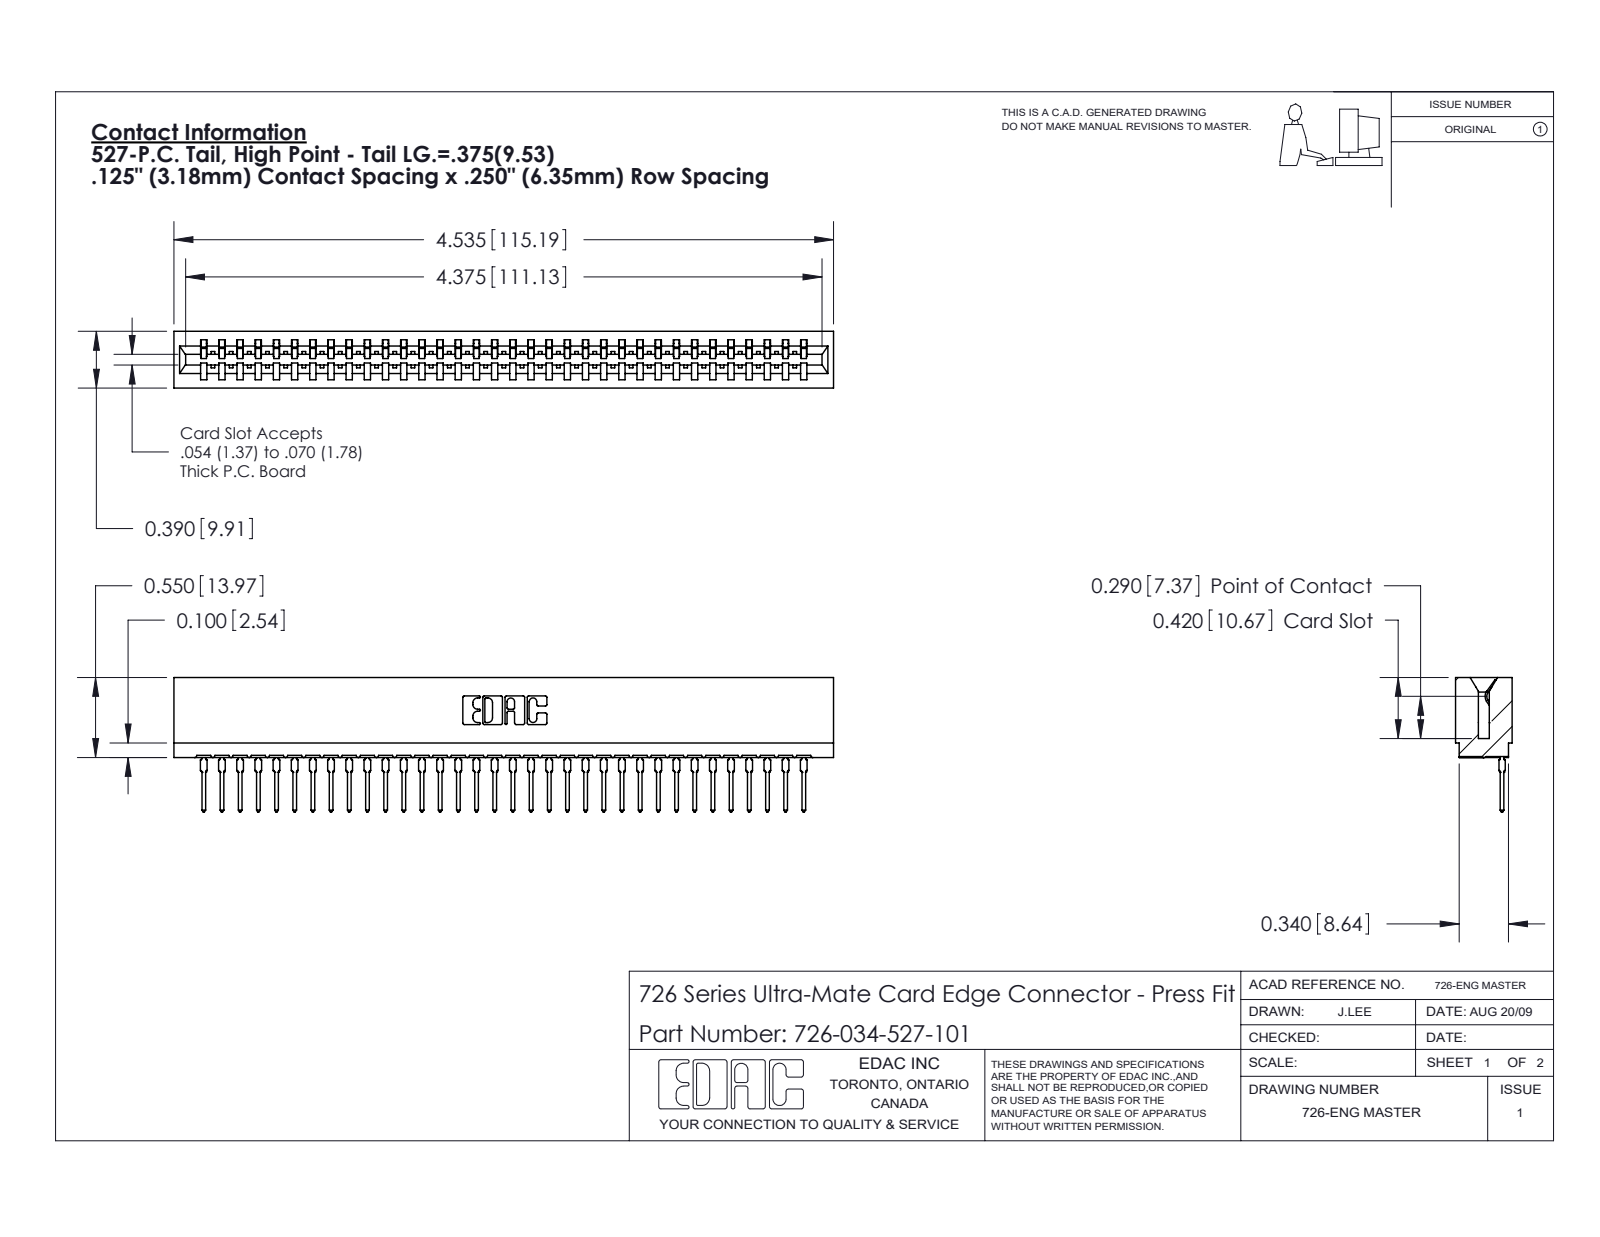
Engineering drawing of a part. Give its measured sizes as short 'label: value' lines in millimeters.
name: 726 Part_.515 Slot Depth - 01; 746-292-001_527; 726-034-527-101
written by: SolidWorks 2020 (CONFIG_CONTROL_DESIGN)
unit: mm
bodies: 35 solids, 3769 faces (2197 planar, 688 cylindrical, 884 other)
size: 115.2 × 23.5 × 9.9
volume: 10 400 mm³; area: 15 890 mm²
rounds: 68× R0.5, 35× R0.4, 22× R0.3, 6× R0.2, 6× R0.8, 4× R0.1, 4× R0.3, 3× R0.7
face distances: 1.4, 8.5, 9.9, 0.6, 7.8, 6.4, 2.1, 7, 9.3, 0.8
